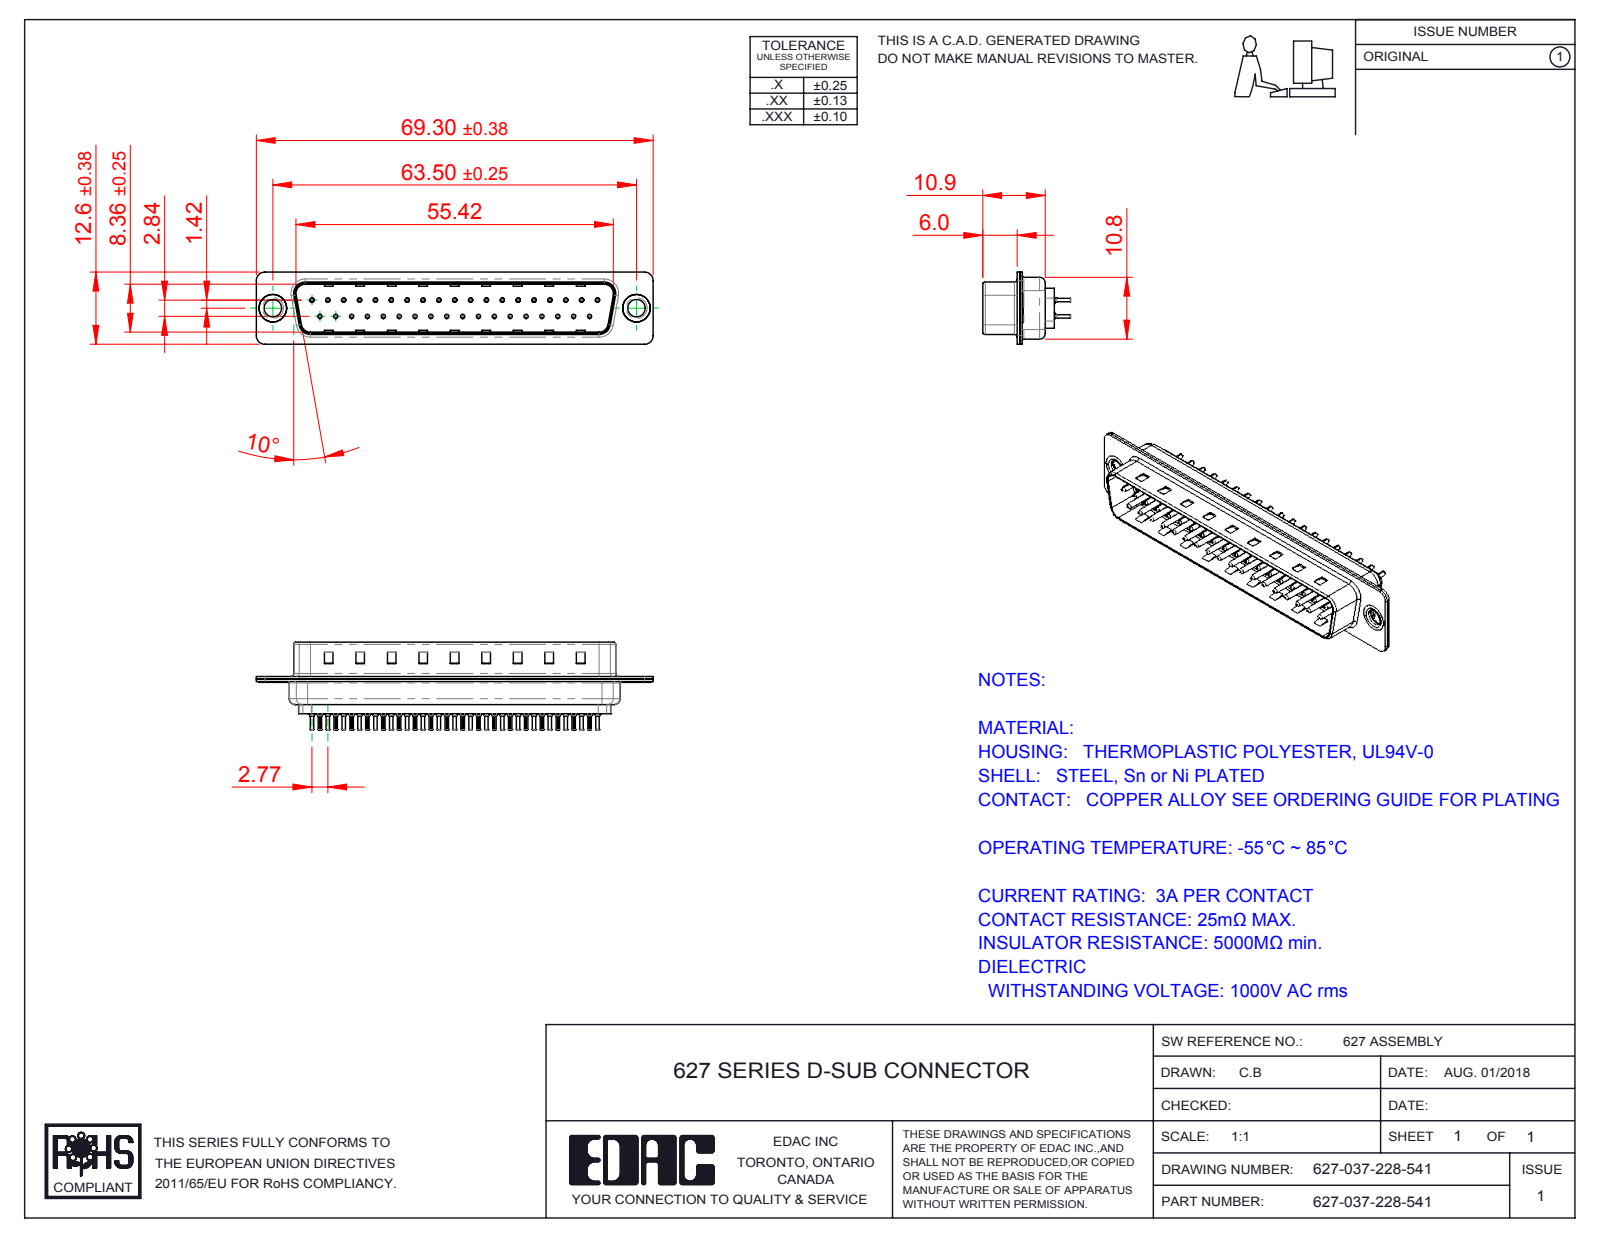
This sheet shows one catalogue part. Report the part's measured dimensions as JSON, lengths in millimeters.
{"part_name": "627-037-228-541; 627 Contact Row 2_28L; 627 Housing_37 LP; 627 Shell Rear_37 Contacts (+3 more)", "step_written_by": "SolidWorks 2016 (CONFIG_CONTROL_DESIGN)", "units": "millimeters", "bodies": {"solids": 42, "faces": 4012, "planar": 1091, "cylindrical": 1494, "other": 1427}, "overall_size": [69.3, 15.3, 12.6], "volume_mm3": 3605, "surface_area_mm2": 10323, "round_holes": [[0.2, 37], [0.35, 37], [1.1, 37], [1.6, 37], [3.05, 2], [4, 2], [4.8, 2]], "round_bosses_or_shafts": [[2, 37], [1.5, 37], [0.75, 37], [0.6, 37], [5, 2], [4.9, 2], [3.55, 2]], "partial_cylinders_radius": [[0.1, 74], [1.5, 16], [2, 12], [0.5, 8], [1.6, 8], [0.25, 4], [0.6, 4], [0.65, 4]], "face_to_face_distances": [0.4, 0.82, 9.58, 0.45, 8.76, 1.5, 0.9, 1.4, 6.05, 0.5], "hole_center_spacings": [3.16, 2.77, 5.54, 8.31, 5.04, 10.1, 11.08, 12.78]}
